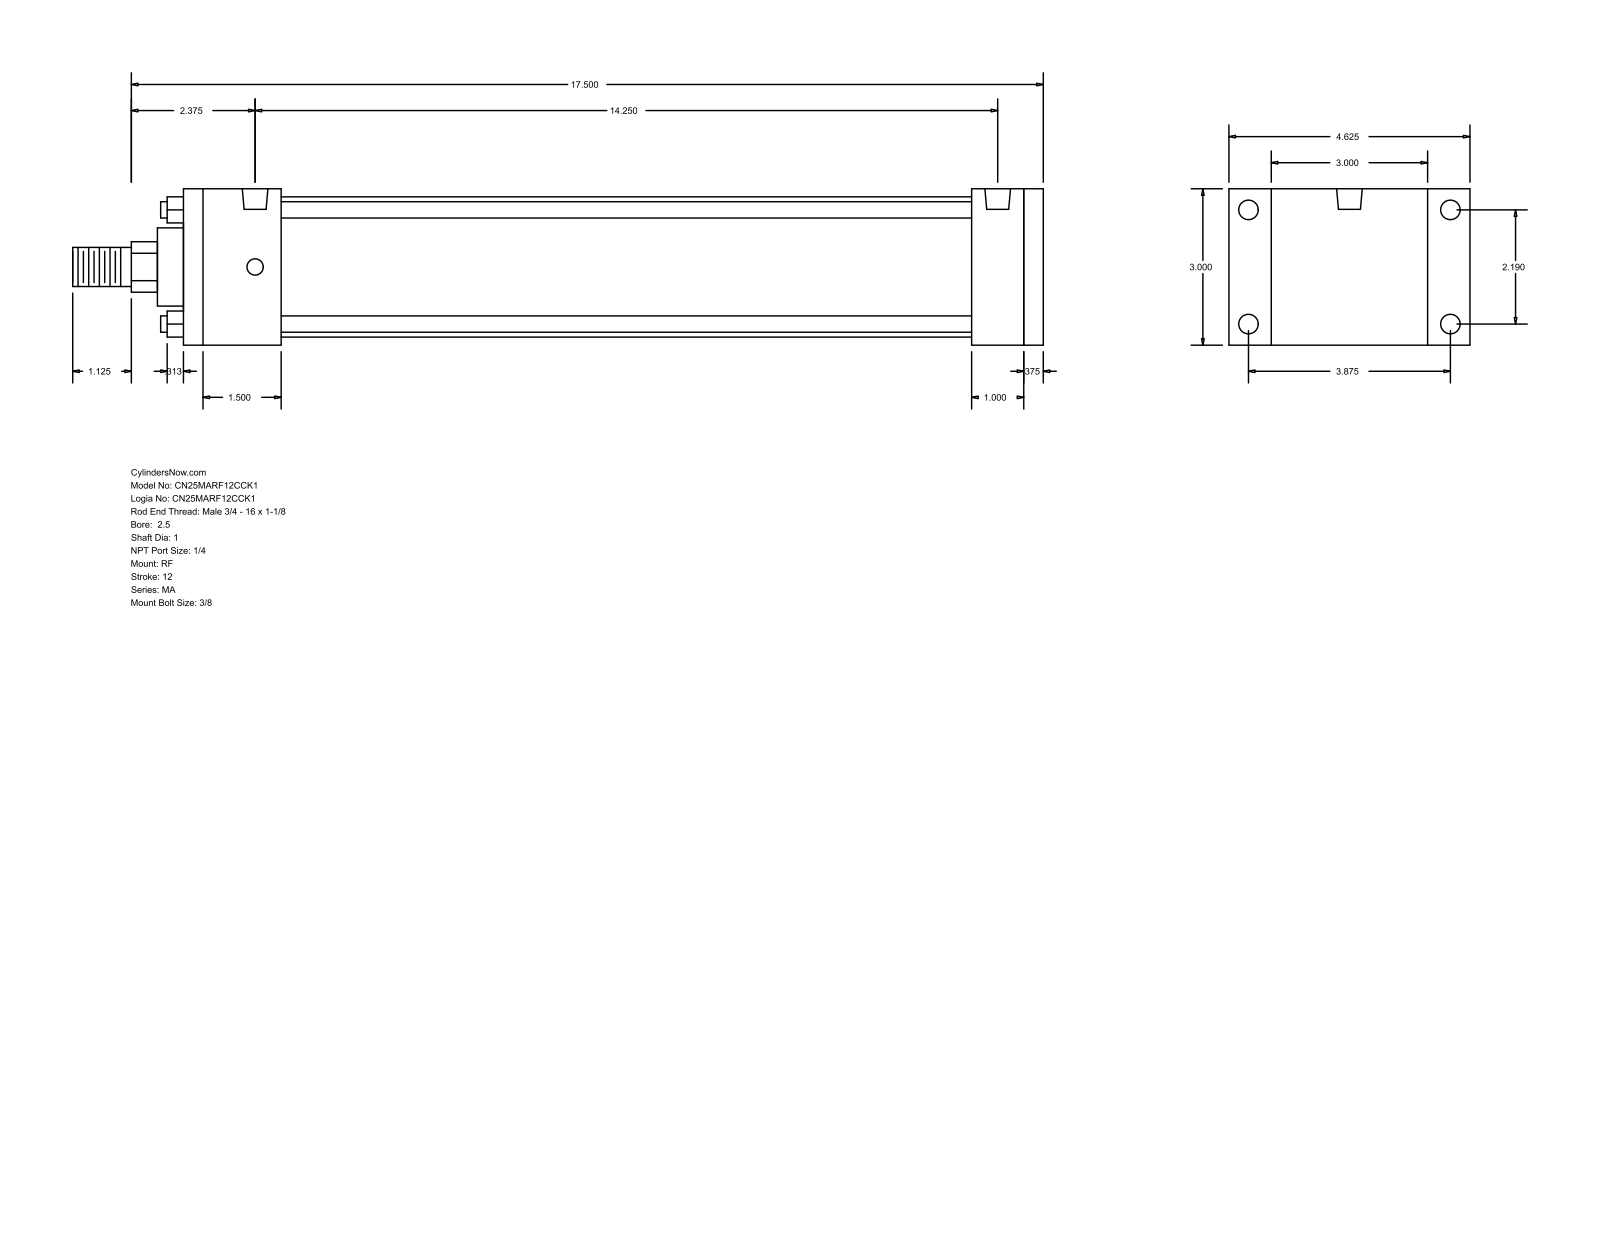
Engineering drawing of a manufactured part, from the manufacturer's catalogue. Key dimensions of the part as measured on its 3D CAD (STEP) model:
Part name (STEP PRODUCT): MA_RF__0250_1
STEP written by: GSSL Pune (CONFIG_CONTROL_DESIGN)
Units: millimetres
Bodies: 0 solids, 92 faces (64 planar, 28 cylindrical, 0 other)
Overall size (bounding box): 473.07 × 117.47 × 76.2
Round holes (diameter × count): ⌀7.94 ×4, ⌀9.53 ×4, ⌀12.49 ×2
Round bosses / shafts (diameter × count): ⌀7.94 ×4, ⌀68.33 ×1, ⌀38.1 ×1, ⌀25.4 ×1, ⌀19.05 ×1
Partial cylindrical surfaces — rounded edges, fillets, slot ends (radius × count): R12.29 ×1
Main face-to-face distances: 76.2, 419.1, 409.58, 9.52, 47.63, 384.17, 336.54, 361.95, 371.47, 25.41
Hole centre spacings: 55.62, 98.42, 113.05, 361.94
